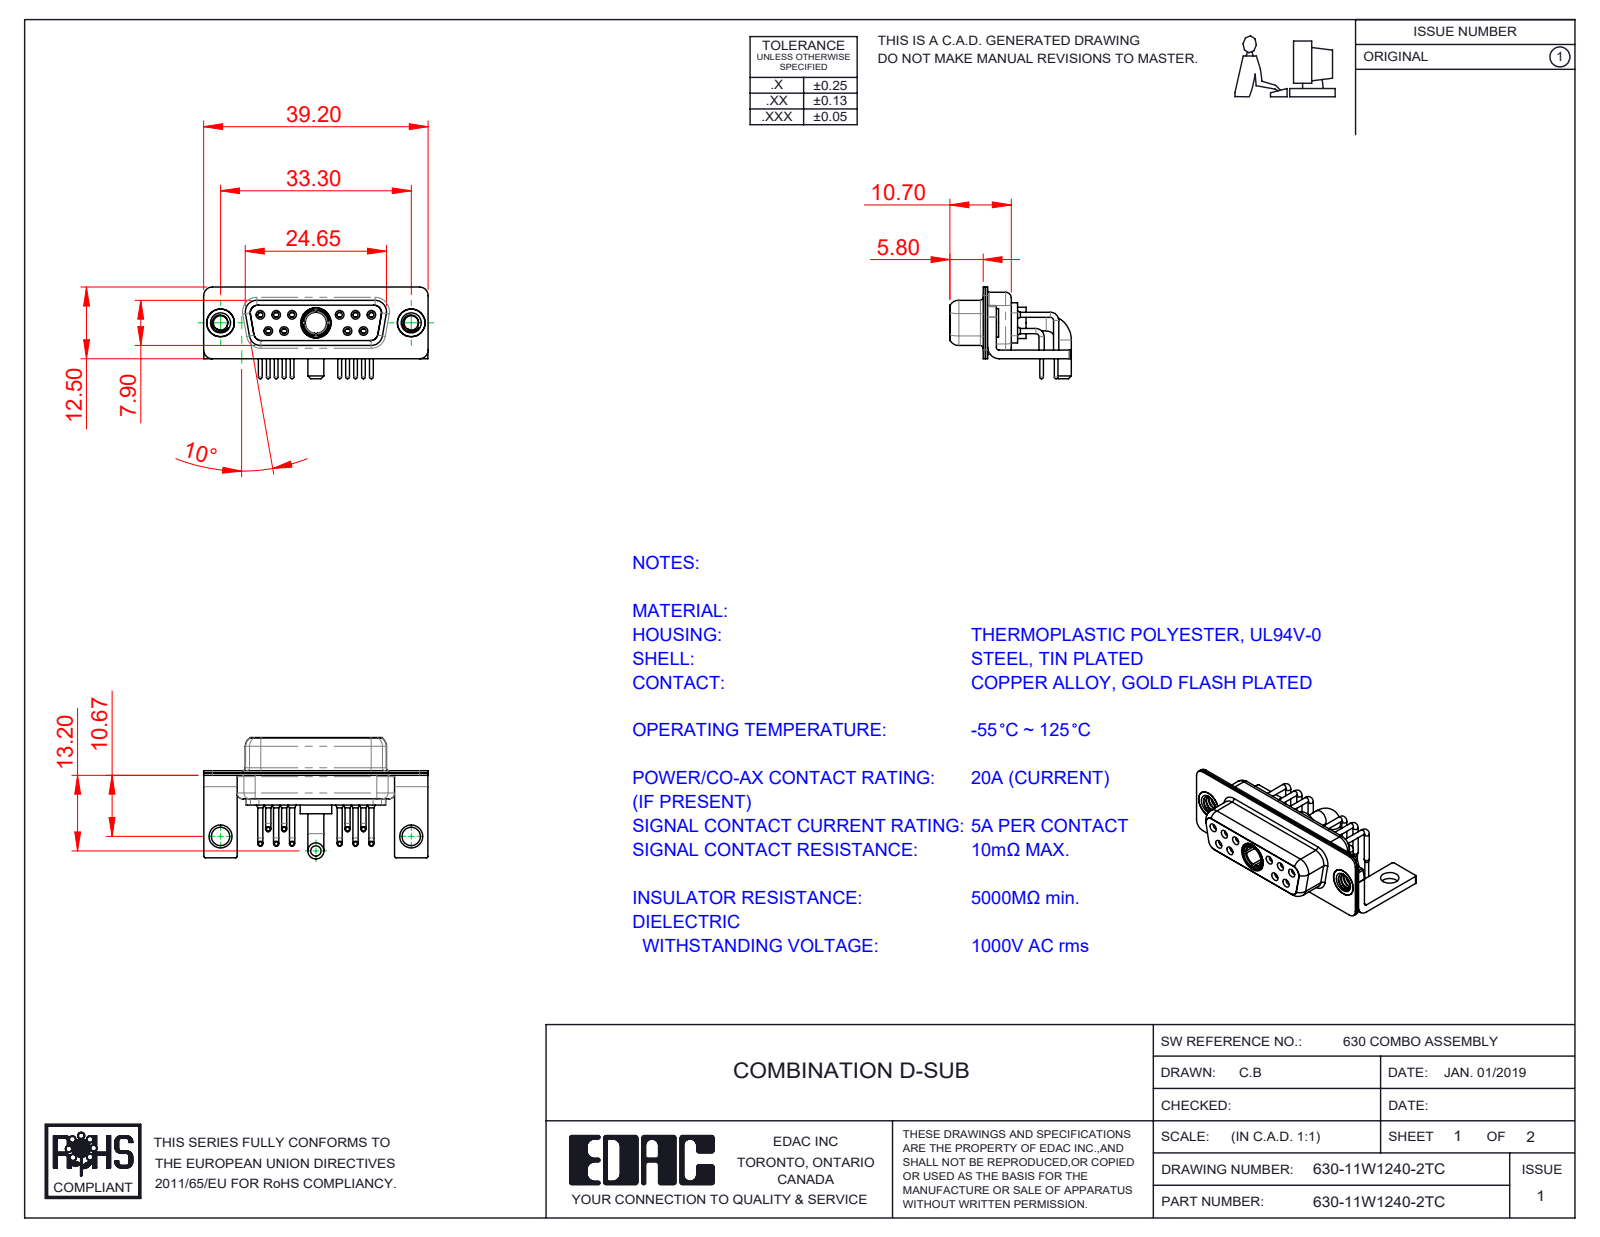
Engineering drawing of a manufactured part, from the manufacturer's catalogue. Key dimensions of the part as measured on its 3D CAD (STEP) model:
Part name (STEP PRODUCT): 630Combo Shell Rear_15 Contacts; Power Socket_20A RA; 630Combo Contact Row 1; 630Combo Contact Row 2 (+5 more)
STEP written by: SolidWorks 2020 (CONFIG_CONTROL_DESIGN)
Units: millimetres
Bodies: 19 solids, 925 faces (266 planar, 410 cylindrical, 249 other)
Overall size (bounding box): 39.2 × 21.2 × 16
Volume: 2 908 mm³ · Surface area: 6 860 mm²
Round holes (diameter × count): ⌀0.9 ×10, ⌀1.1 ×10, ⌀1.5 ×10, ⌀2 ×10, ⌀1.7 ×6, ⌀1.6 ×4, ⌀4.85 ×3, ⌀2.5 ×2, ⌀3.2 ×2, ⌀4 ×2, ⌀4.05 ×2, ⌀3.7 ×1
Round bosses / shafts (diameter × count): ⌀0.9 ×10, ⌀0.65 ×10, ⌀1.6 ×6, ⌀5 ×2, ⌀4.95 ×2, ⌀4.8 ×2, ⌀2.8 ×2, ⌀5.5 ×1
Partial cylindrical surfaces — rounded edges, fillets, slot ends (radius × count): R0.25 ×16, R1.5 ×16, R2 ×13, R1.35 ×12, R1.6 ×8, R0.5 ×5, R0.6 ×4, R0.65 ×4
Main face-to-face distances: 0.4, 0.8, 1.4, 0.45, 8.45, 1.5, 1.8, 8.9, 6.2, 2.3
Hole centre spacings: 3.16, 2.77, 13.85, 11.08, 16.62, 5.03, 5.04, 5.54
